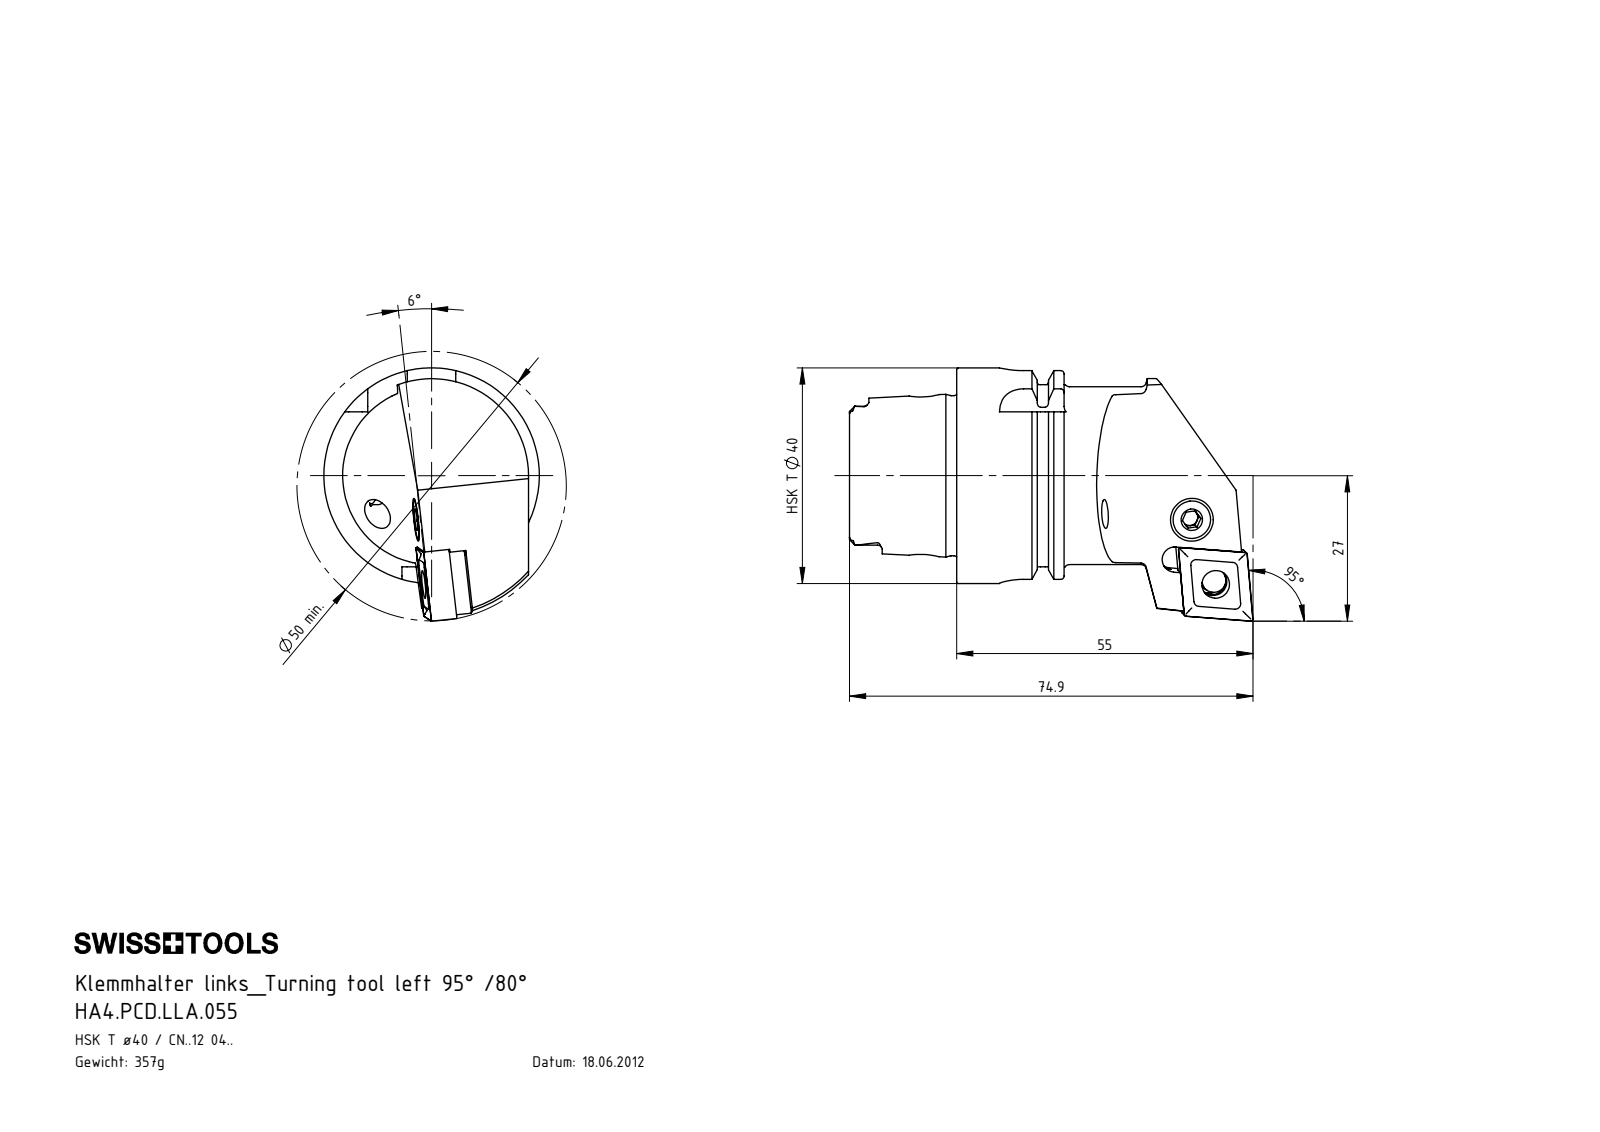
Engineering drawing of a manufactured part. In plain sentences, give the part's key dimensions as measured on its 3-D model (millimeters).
The part is named "HA4-PCD.LLA.055; WCD-ER4.101.017_A; WCD-ER3.101.000_A; WCD-ER1.101.000 (+4 more)". Its 3-D file was written by "SolidWorks 2012 (CONFIG_CONTROL_DESIGN)". It is 8 solids with 393 faces: 124 planar, 109 cylindrical and 160 other. Overall it measures 74.9 by 47 by 40 millimeters. Its volume is 44 612 cubic millimeters and its surface area 16 278 square millimeters. Round holes: 2 of diameter 4.2, 2 of diameter 5, 1 of diameter 4, 1 of diameter 4.6, 1 of diameter 5.16, 1 of diameter 6.4, 1 of diameter 7, 1 of diameter 8.4, 1 of diameter 10, 1 of diameter 11, 1 of diameter 12.5, 1 of diameter 21. Round bosses or shafts: 1 of diameter 40, 1 of diameter 34.75, 1 of diameter 33, 1 of diameter 29.71, 1 of diameter 8, 1 of diameter 7.9, 1 of diameter 6.4, 1 of diameter 5. Partial cylindrical surfaces (rounded edges, fillets, slot ends): 6 of radius 0.9, 4 of radius 0.4, 4 of radius 1, 4 of radius 1.88, 4 of radius 4.5, 2 of radius 2.5, 1 of radius 0.8, 1 of radius 2.1. The main face-to-face distances are 4.46, 7.95, 19.95, 12, 7.64, 3.18, 19.9, 27.85, 39.85, 35.7. The hole center spacings are 12.8, 12.85.
